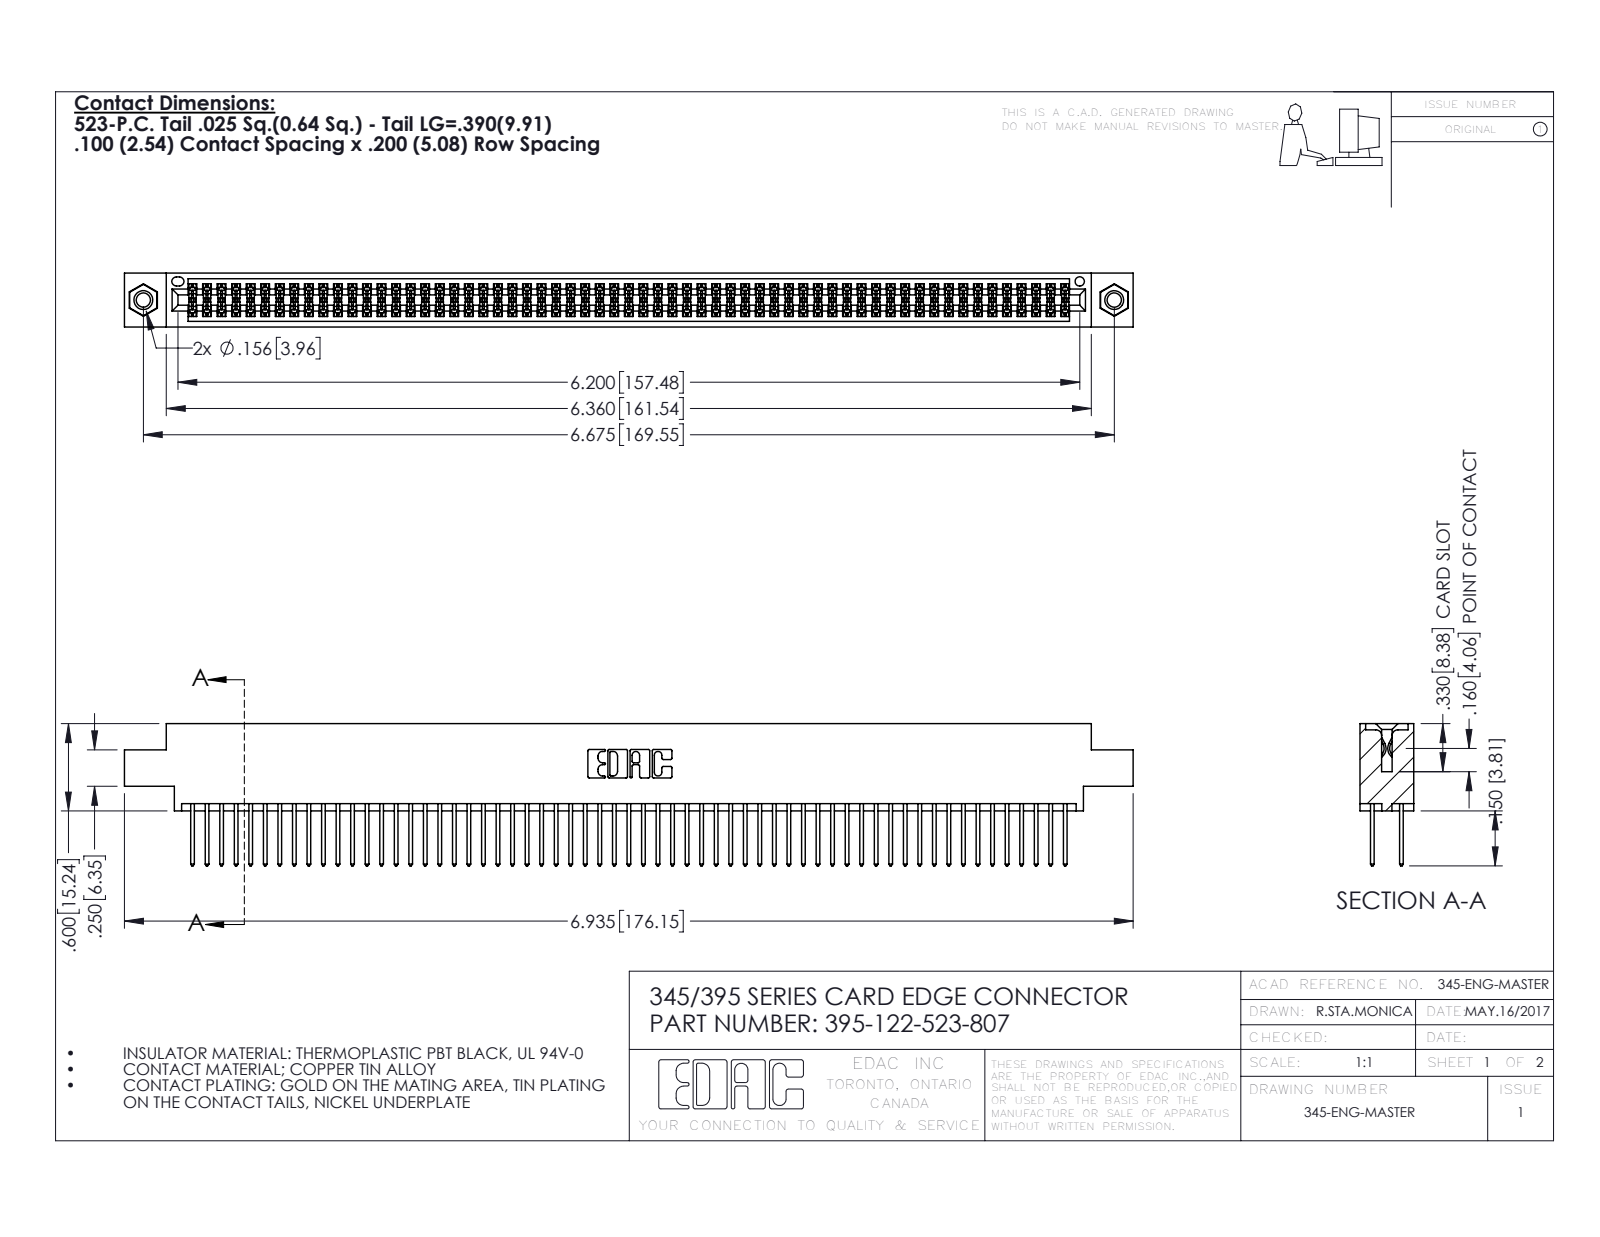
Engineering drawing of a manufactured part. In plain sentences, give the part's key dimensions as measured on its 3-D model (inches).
The part is named "345-250-001_345-250-005-103; 345 Part_0.170 Offset - 0.156 Dia-TI; 395-122-523-807; 345-292-001_345-293-123". Its 3-D file was written by "SolidWorks 2016 (CONFIG_CONTROL_DESIGN)". It is 125 solids with 6290 faces: 4142 planar, 2132 cylindrical and 16 other. Overall it measures 6.935 by 0.977 by 0.37 inches. Its volume is 1.062 cubic inches and its surface area 42.47 square inches. Round holes: 2 of diameter 0.098, 2 of diameter 0.125, 2 of diameter 0.156, 1 of diameter 0.064. Round bosses or shafts: 2 of diameter 0.155. Partial cylindrical surfaces (rounded edges, fillets, slot ends): 183 of radius 0.006, 122 of radius 0.01, 22 of radius 0.01, 6 of radius 0.007, 6 of radius 0.031, 3 of radius 0.026, 2 of radius 0.014, 2 of radius 0.019. The main face-to-face distances are 0.072, 0.298, 0.2, 0.098, 0.272, 0.025, 0.37, 0.225, 0.175, 0.149. The hole center spacings are 0.27, 6.439, 6.675.
